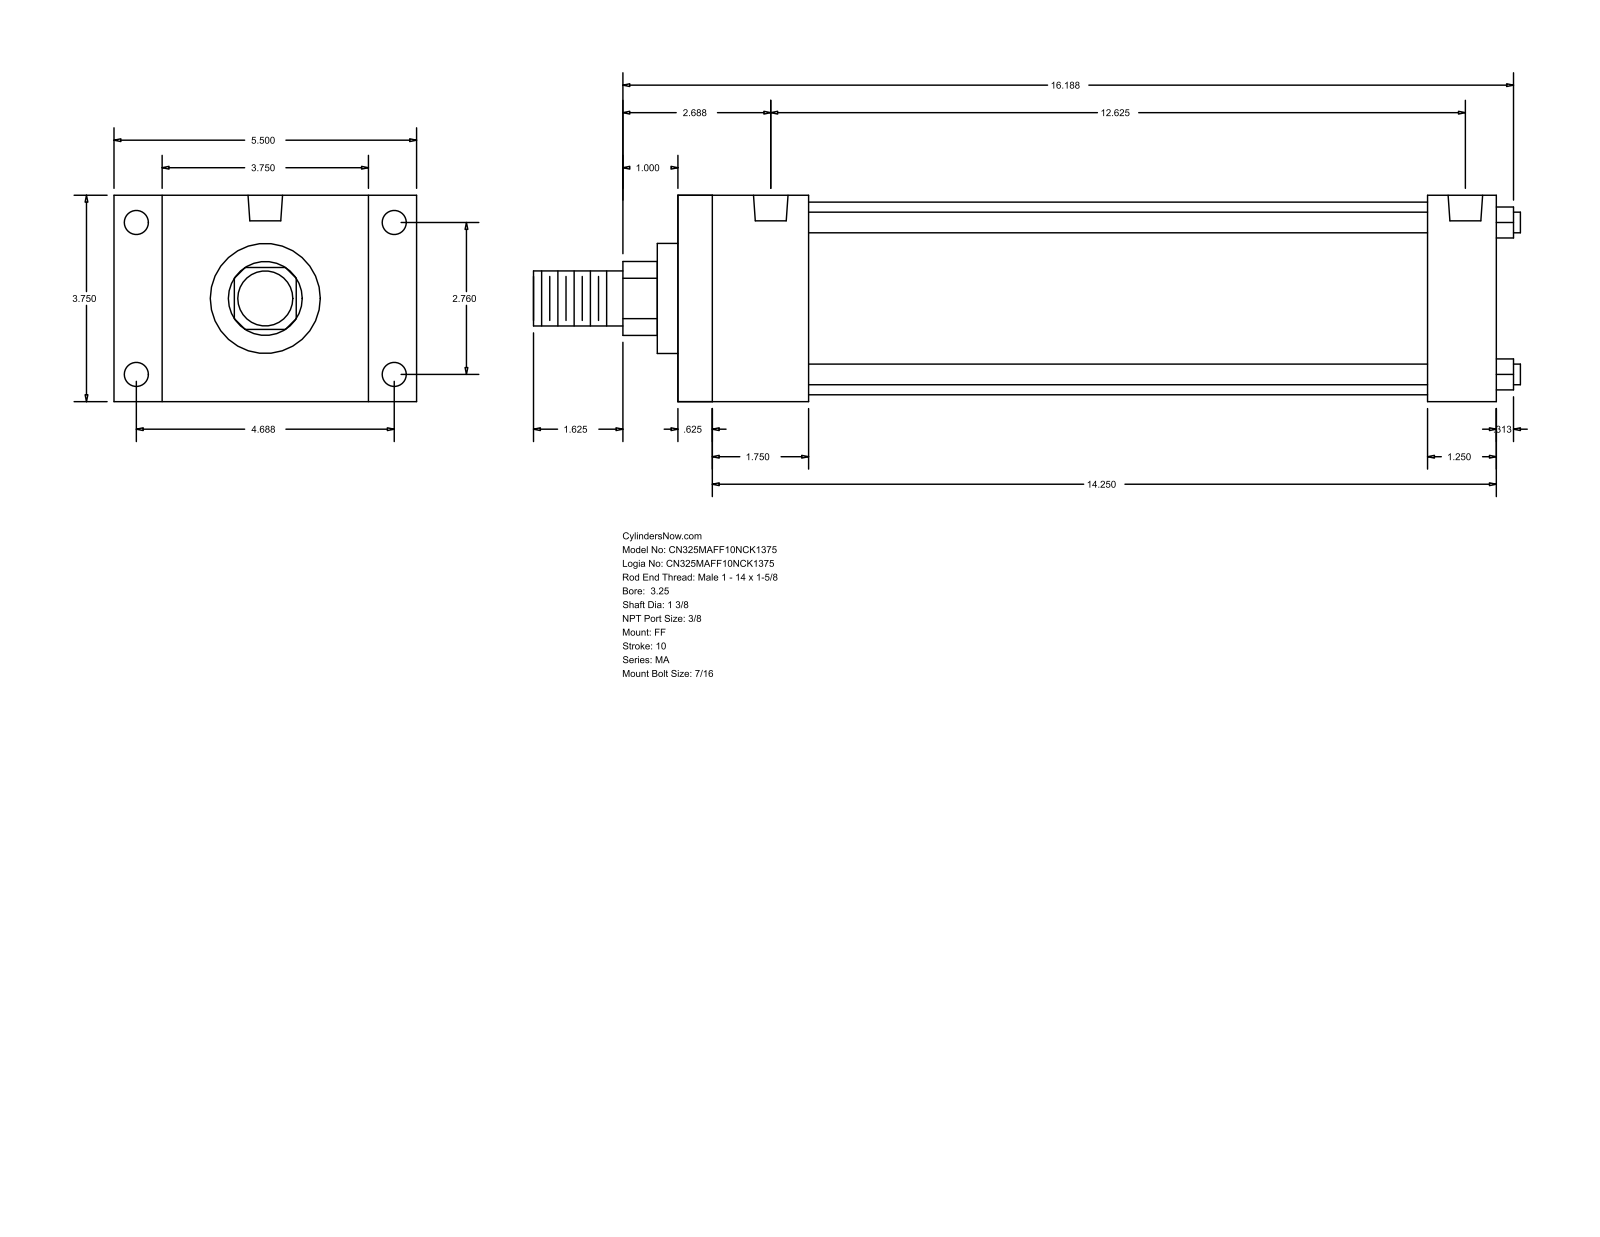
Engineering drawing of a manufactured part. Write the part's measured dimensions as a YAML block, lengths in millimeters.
part_name: "MA_FF__0325_1.375"
step_written_by: "GSSL Pune (CONFIG_CONTROL_DESIGN)"
units: millimeters
bodies: {solids: 0, faces: 92, planar: 64, cylindrical: 28, other: 0}
overall_size: [455.61, 139.7, 95.25]
round_holes:
  - {diameter: 11.11, count: 8}
  - {diameter: 15.93, count: 2}
round_bosses_or_shafts:
  - {diameter: 9.53, count: 4}
  - {diameter: 88.9, count: 1}
  - {diameter: 50.8, count: 1}
  - {diameter: 34.92, count: 1}
  - {diameter: 25.4, count: 1}
partial_cylinders:
  - {radius: 17.06, count: 1}
face_to_face_distances: [95.24, 377.83, 15.87, 361.96, 22.23, 117.47, 60.32, 346.08, 44.45, 330.21]
hole_center_spacings: [70.1, 119.06, 138.16, 311.15, 4.76, 4.77, 315.91, 315.92]
